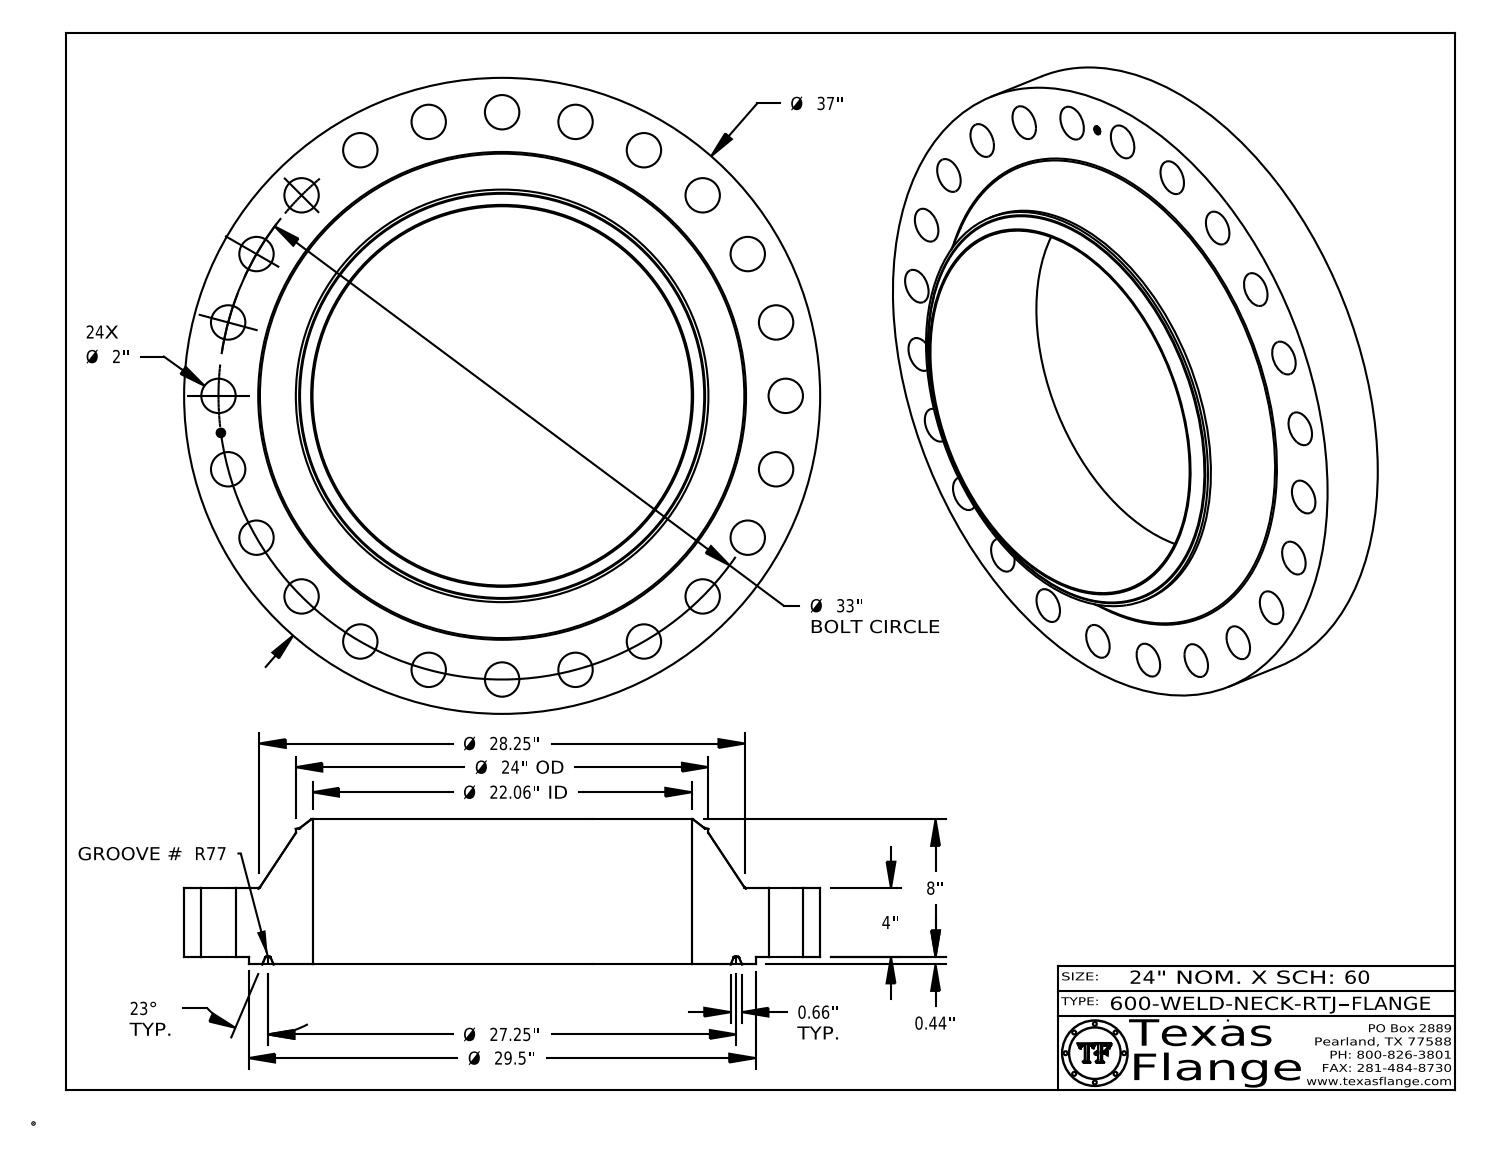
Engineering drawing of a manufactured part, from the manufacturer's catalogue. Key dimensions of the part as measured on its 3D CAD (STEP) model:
Part name (STEP PRODUCT): 600-WELD-NECK-RTJ
STEP written by: CATIA V5 STEP AP214 (AUTOMOTIVE_DESIGN)
Units: inches
Bodies: 1 solid, 465 faces (371 planar, 76 cylindrical, 18 other)
Overall size (bounding box): 37 × 37 × 8.438
Volume: 3 116 in³ · Surface area: 3 148 in²
Round holes (diameter × count): ⌀2 ×24, ⌀0.495 ×1, ⌀22.062 ×1
Round bosses / shafts (diameter × count): ⌀0.03 ×8, ⌀37 ×1, ⌀29.5 ×1, ⌀24 ×1, ⌀0.39 ×1
Main face-to-face distances: 4, 0.438, 4.438, 8.438, 8, 0.015, 4.423, 3.985, 4.015, 0.07
Hole centre spacings: 16.5, 4.307, 8.541, 20.089, 23.335, 26.181, 31.876, 32.718
